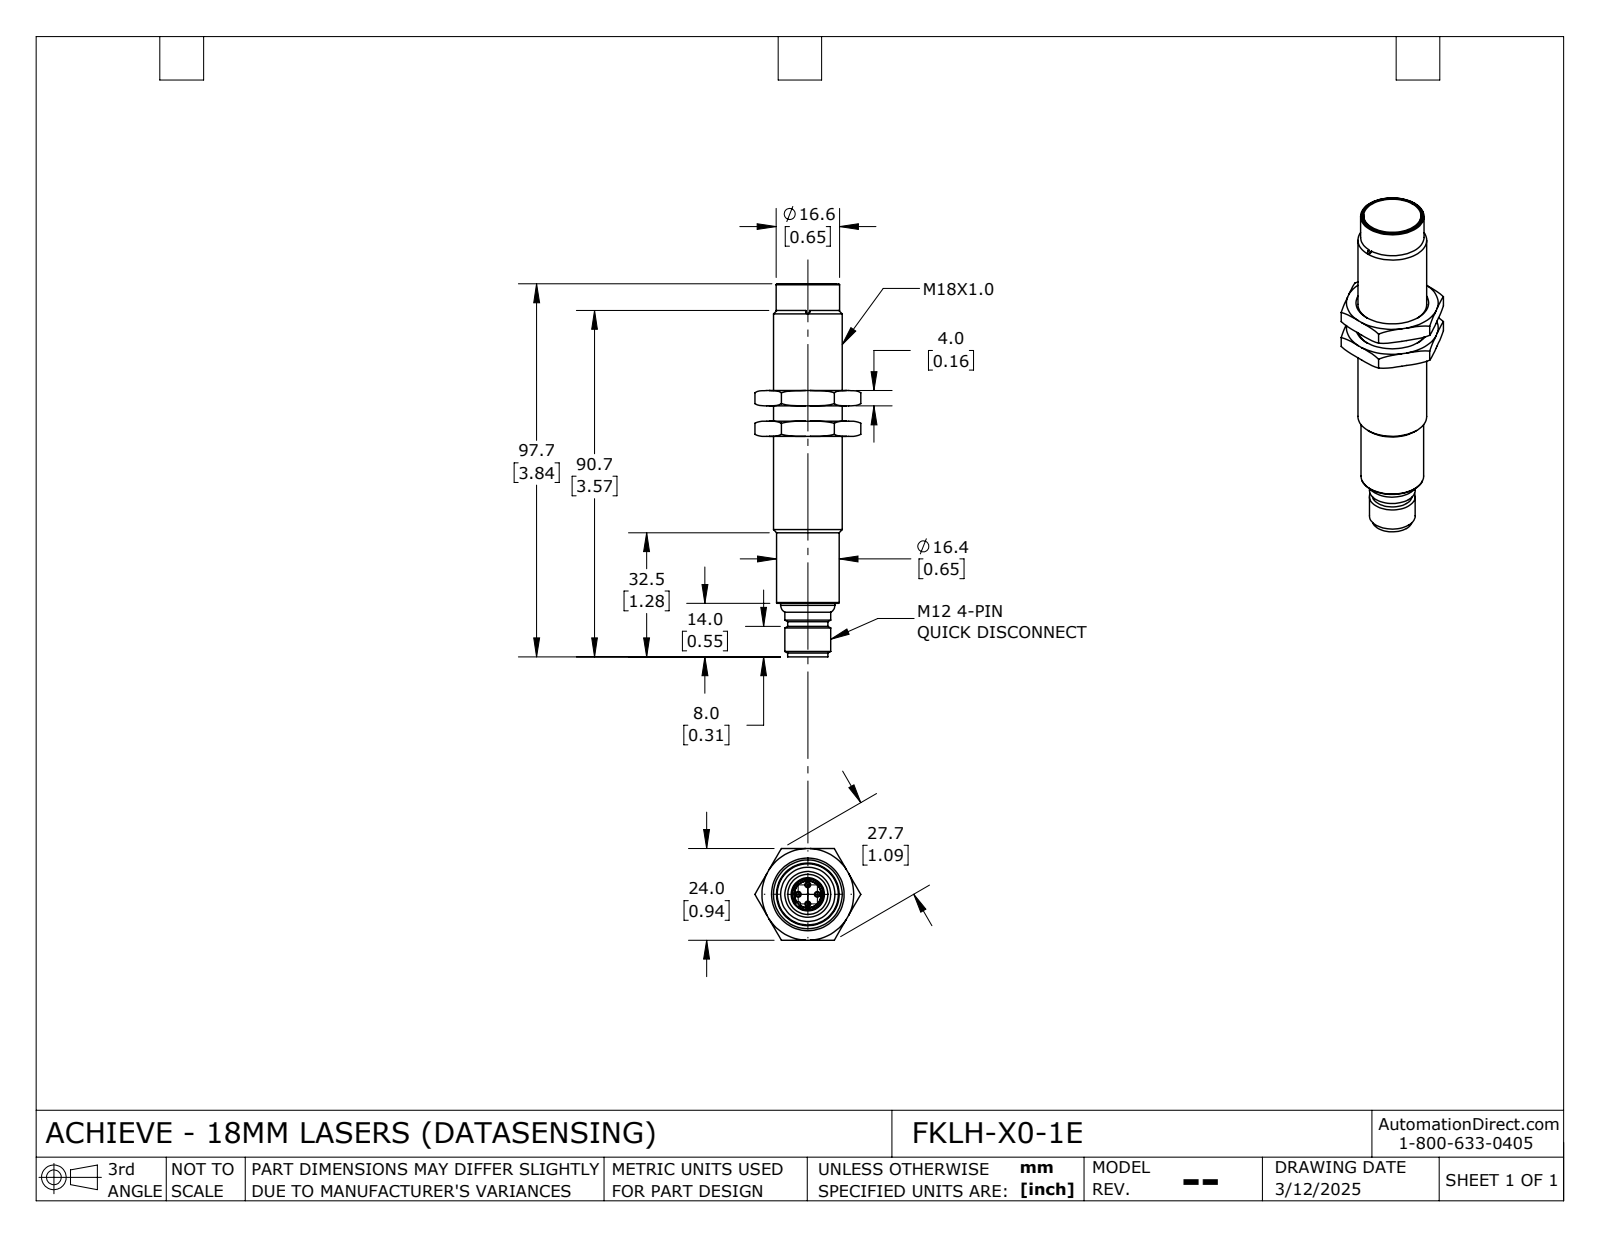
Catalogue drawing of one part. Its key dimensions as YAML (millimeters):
part_name: "FKLH-X0-1E_Default"
step_written_by: "SolidWorks 2024 (CONFIG_CONTROL_DESIGN)"
units: millimeters
bodies: {solids: 3, faces: 113, planar: 41, cylindrical: 24, other: 48}
overall_size: [97.6, 27.7, 24]
volume: 23070
surface_area: 8974
round_holes:
  - {diameter: 7.1, count: 1}
  - {diameter: 8.3, count: 1}
  - {diameter: 14.9, count: 1}
  - {diameter: 18, count: 1}
round_bosses_or_shafts:
  - {diameter: 1, count: 4}
  - {diameter: 16.6, count: 1}
  - {diameter: 16.4, count: 1}
  - {diameter: 15, count: 1}
  - {diameter: 14.8, count: 1}
  - {diameter: 14.2, count: 1}
  - {diameter: 12, count: 1}
  - {diameter: 10.5, count: 1}
partial_cylinders:
  - {radius: 0.5, count: 2}
  - {radius: 0.6, count: 1}
  - {radius: 7.5, count: 1}
face_to_face_distances: [4, 8, 24, 2.4, 2.5, 12, 33.4, 33.6, 35.9, 25.4]
